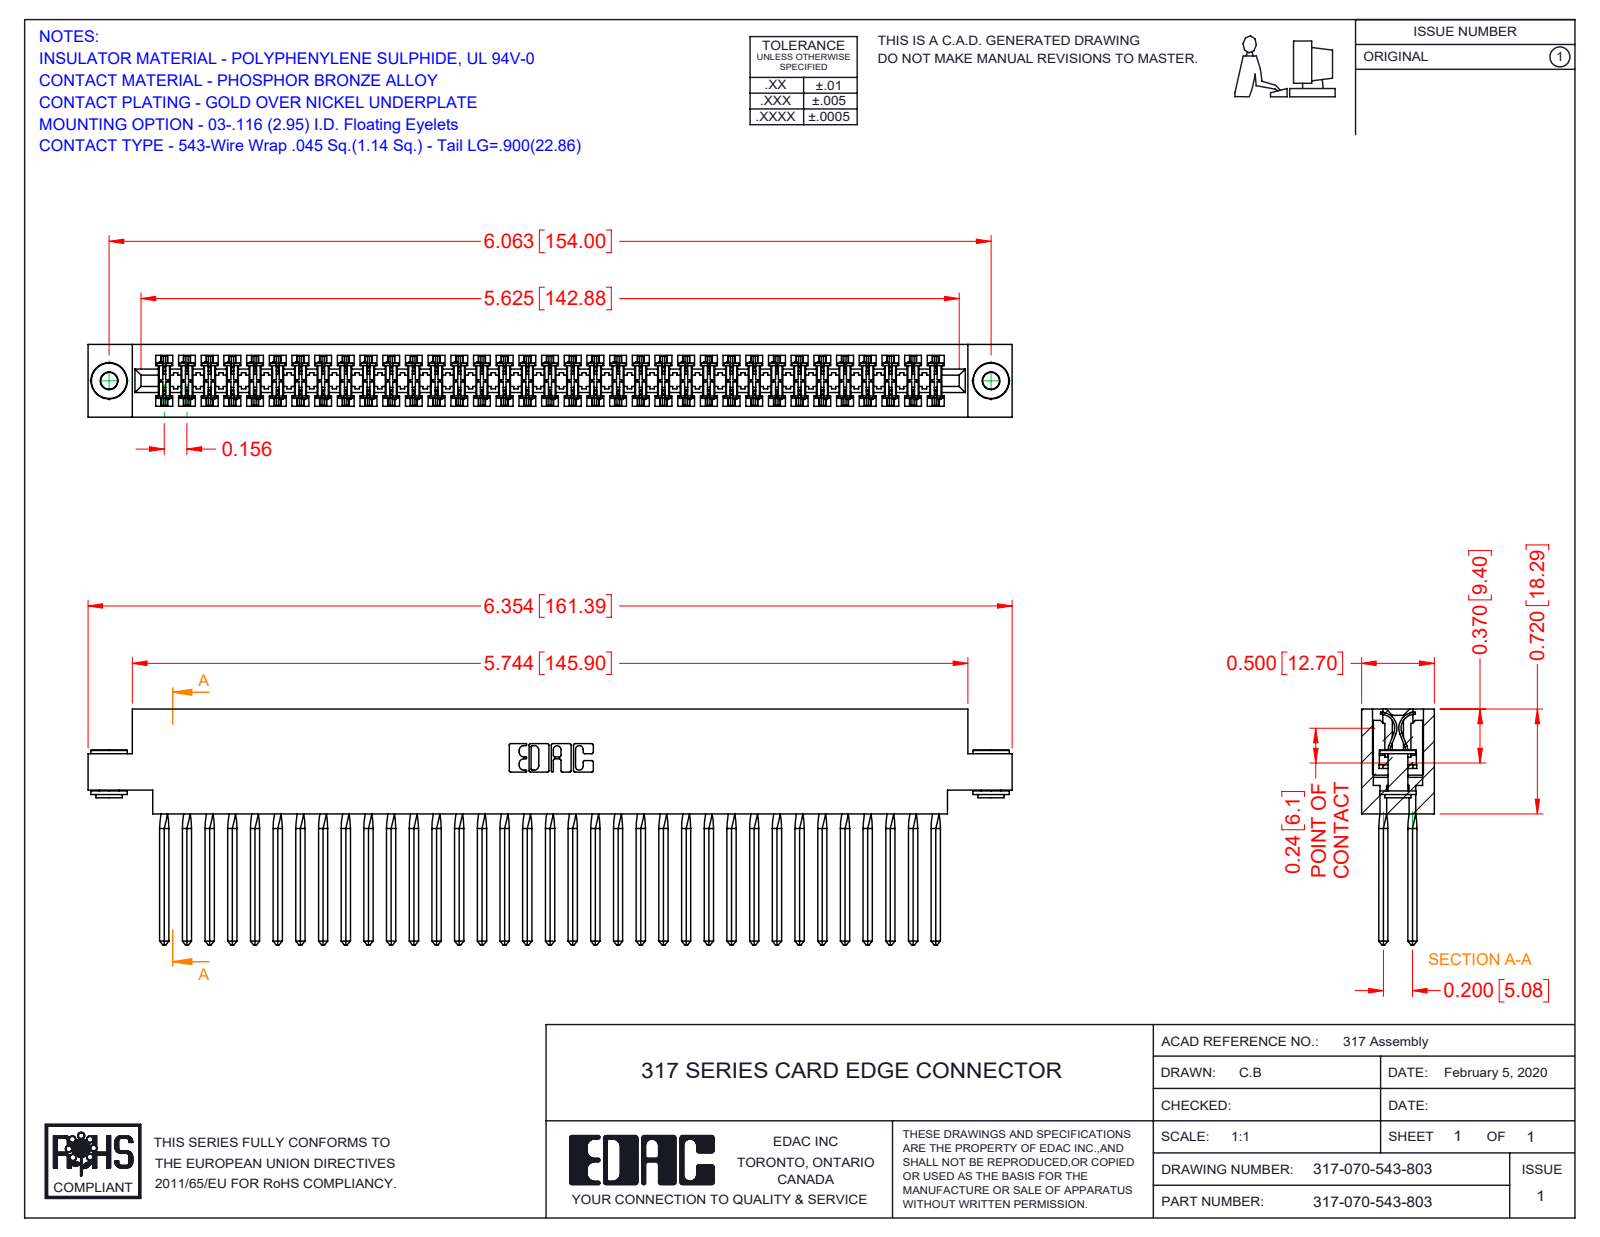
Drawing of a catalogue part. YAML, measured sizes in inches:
part_name: "345-250-002_345-250-002-102; 317 Part_.156 Dia - TH; 317-070-543-803; 317-290-001_543"
step_written_by: "SolidWorks 2016 (CONFIG_CONTROL_DESIGN)"
units: inches
bodies: {solids: 73, faces: 6370, planar: 5178, cylindrical: 904, other: 288}
overall_size: [6.354, 1.62, 0.5]
volume: 1.661
surface_area: 63.9
round_holes:
  - {diameter: 0.116, count: 2}
  - {diameter: 0.156, count: 2}
round_bosses_or_shafts:
  - {diameter: 0.25, count: 2}
  - {diameter: 0.18, count: 2}
  - {diameter: 0.136, count: 2}
partial_cylinders:
  - {radius: 0.015, count: 140}
  - {radius: 0.01, count: 22}
  - {radius: 0.007, count: 6}
  - {radius: 0.031, count: 6}
  - {radius: 0.026, count: 3}
  - {radius: 0.095, count: 2}
  - {radius: 0.1, count: 2}
  - {radius: 0.11, count: 2}
face_to_face_distances: [0.5, 0.075, 0.425, 0.35, 0.11, 0.195, 0.094, 0.2, 0.115, 0.131]
hole_center_spacings: [6.063]
